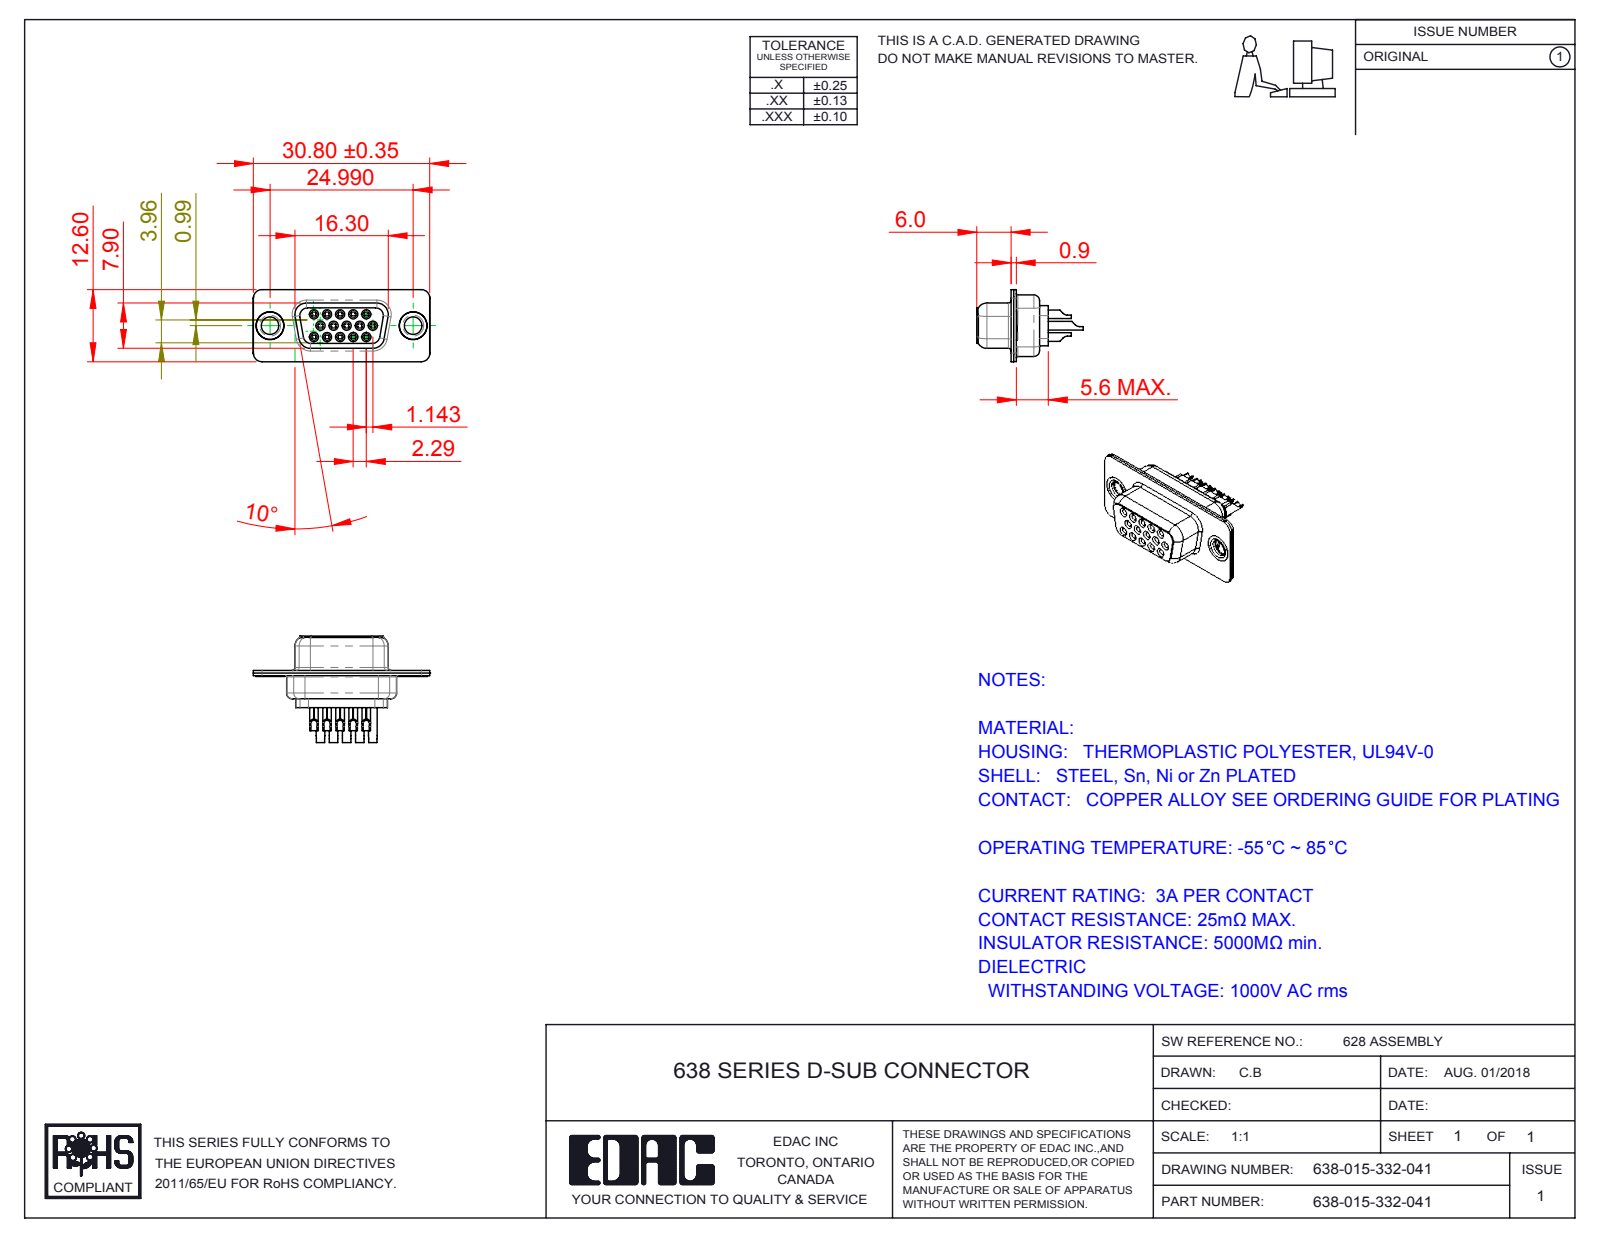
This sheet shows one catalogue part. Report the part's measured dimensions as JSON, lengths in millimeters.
{"part_name": "638 Contact Row 2_32L; 638 Shell Rear_15 Contacts; 638 Housing_15 Contacts; 638 Contact Row 3_32L (+4 more)", "step_written_by": "SolidWorks 2016 (CONFIG_CONTROL_DESIGN)", "units": "millimeters", "bodies": {"solids": 20, "faces": 1588, "planar": 382, "cylindrical": 496, "other": 710}, "overall_size": [30.81, 18.6, 12.6], "volume_mm3": 1525, "surface_area_mm2": 5715, "round_holes": [[0.8, 15], [1, 15], [1.1, 15], [1.6, 15], [1.7, 15], [1.8, 15], [2, 2], [3.05, 2], [4, 2], [4.05, 2], [4.85, 2]], "round_bosses_or_shafts": [[2, 15], [1.5, 15], [1.2, 15], [5, 2], [4.95, 2], [4.8, 2], [3.55, 2]], "partial_cylinders_radius": [[1.5, 20], [2, 12], [0.28, 10], [1.55, 8], [1, 7], [1.35, 5], [0.25, 4], [0.5, 4]], "face_to_face_distances": [0.45, 0.9, 0.4, 1.43, 8.88, 6.6, 1.4, 2.28, 7.05, 0.85], "hole_center_spacings": [3.96, 2.28, 4.57, 2.29, 6.05, 6.04, 6.86, 7.92]}
